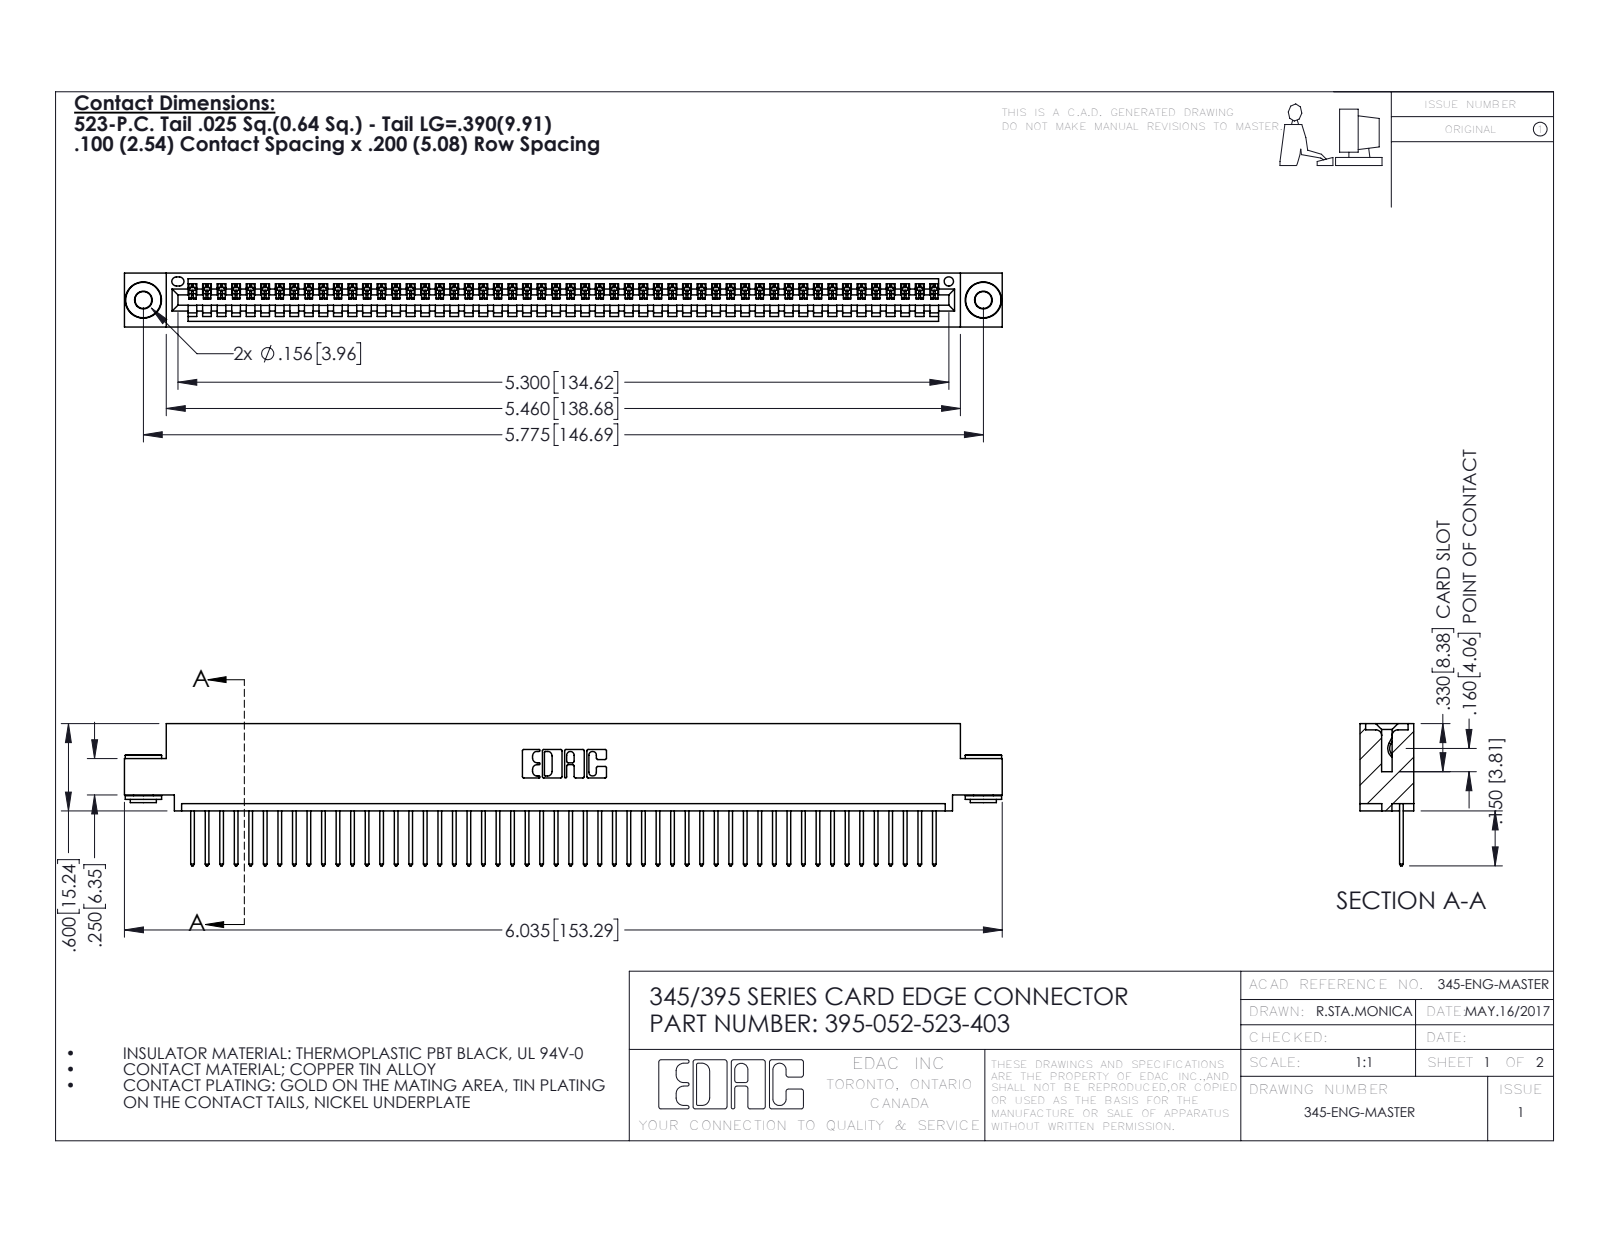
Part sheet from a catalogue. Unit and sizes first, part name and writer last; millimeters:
Units: millimetres
Overall size (bounding box): 153.3 × 24.8 × 9.4
Round holes (diameter × count): ⌀2.9 ×2, ⌀4 ×2, ⌀1.6 ×1
Round bosses / shafts (diameter × count): ⌀6.4 ×2, ⌀4.6 ×2, ⌀3.5 ×2
Partial cylindrical surfaces — rounded edges, fillets, slot ends (radius × count): R0.2 ×104, R0.3 ×104, R0.3 ×22, R0.2 ×6, R0.8 ×6, R0.7 ×3, R0.8 ×2, R1 ×2
Main face-to-face distances: 1.8, 7.6, 9.4, 0.6, 2.5, 6.9, 5.1, 5.7, 3.8, 1.8
Hole centre spacings: 6.9, 140.7, 146.7
Volume: 14 600 mm³ · Surface area: 19 850 mm²
Bodies: 55 solids, 3184 faces (2174 planar, 1002 cylindrical, 8 other)
Part name (STEP PRODUCT): 395-052-523-403; 345 Part_0.110 Offset - 0.156 Dia-TH; 345-292-001_345-293-123; 345-250-002_345-250-002-102
STEP written by: SolidWorks 2016 (CONFIG_CONTROL_DESIGN)
